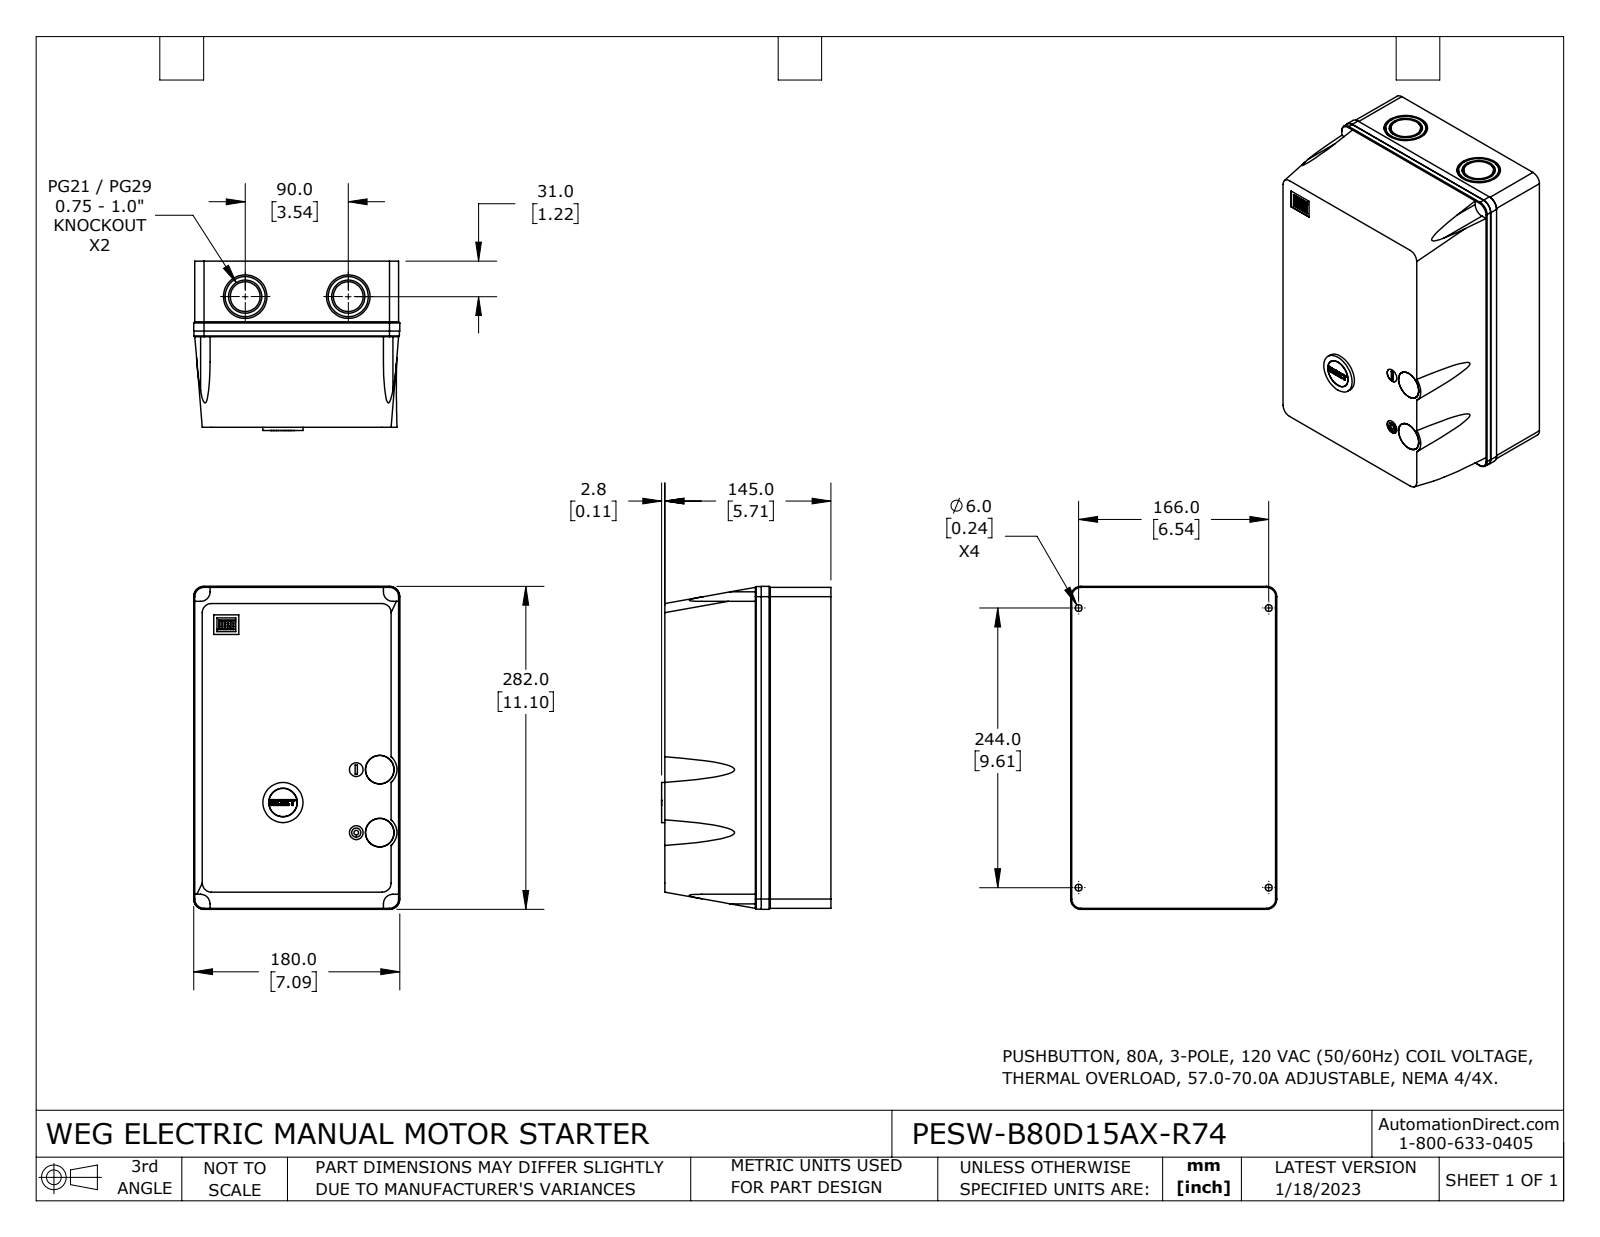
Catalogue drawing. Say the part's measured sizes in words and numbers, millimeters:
The part is named "PESW-B80D15AX-R74". Its 3-D file was written by "SolidWorks 2021 (CONFIG_CONTROL_DESIGN)". It is 3 solids with 286 faces: 130 planar, 144 cylindrical and 12 other. Overall it measures 282 by 180 by 147.9 millimeters. Its volume is 7 014 000 cubic millimeters and its surface area 232 257 square millimeters. Round holes: 4 of diameter 6, 3 of diameter 25, 2 of diameter 12, 2 of diameter 29, 2 of diameter 38, 1 of diameter 4, 1 of diameter 30.5. Round bosses or shafts: 3 of diameter 35, 2 of diameter 26, 2 of diameter 24.8, 1 of diameter 30.3, 1 of diameter 24.6, 1 of diameter 14, 1 of diameter 8. Partial cylindrical surfaces (rounded edges, fillets, slot ends): 34 of radius 0.1, 4 of radius 8, 4 of radius 8.3, 4 of radius 8.7, 4 of radius 9, 1 of radius 1.6. The main face-to-face distances are 145, 178, 280, 1, 0.7, 179, 179.7, 178.7, 281, 180. The hole center spacings are 20.5, 55, 58.7, 166, 244, 295.11, 49.14, 57.14.
